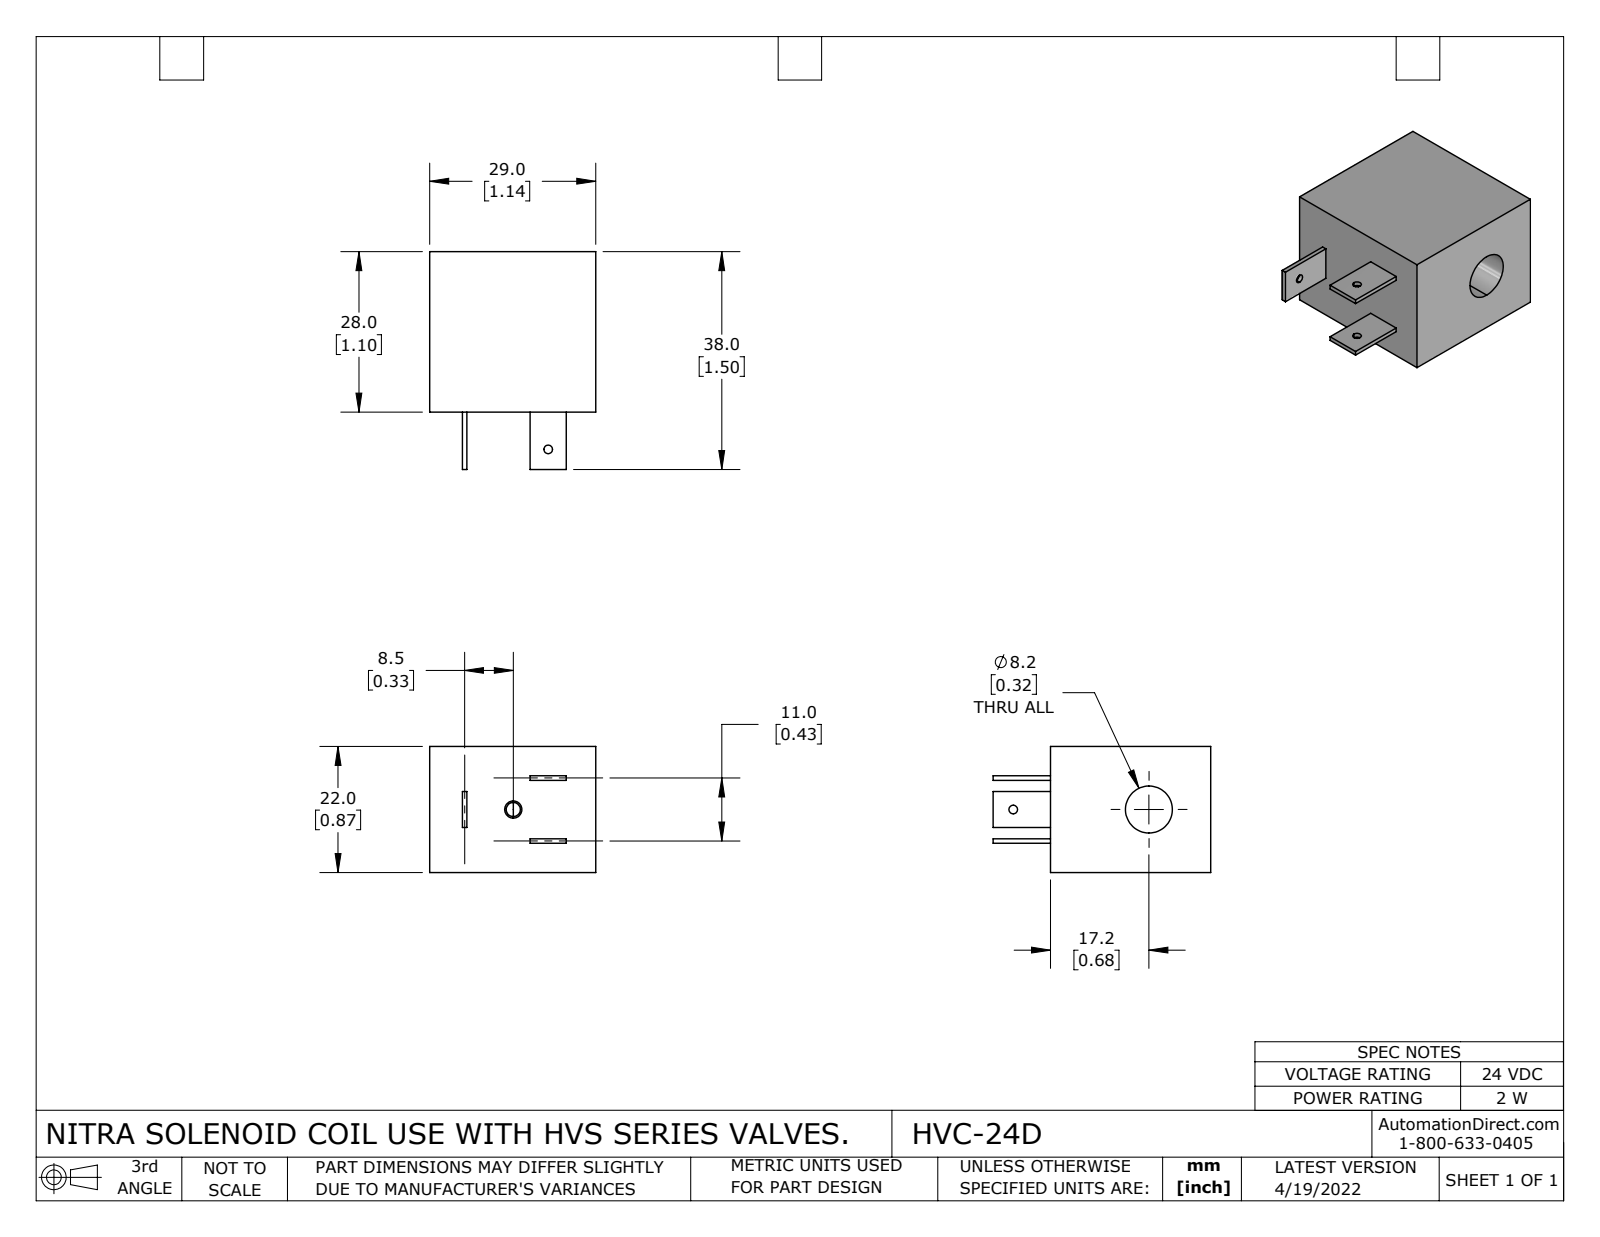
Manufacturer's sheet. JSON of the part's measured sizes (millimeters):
{"part_name": "HVC-24D", "step_written_by": "SolidWorks 2021 (CONFIG_CONTROL_DESIGN)", "units": "millimeters", "bodies": {"solids": 1, "faces": 35, "planar": 21, "cylindrical": 10, "other": 4}, "overall_size": [38, 29, 22], "volume_mm3": 16454, "surface_area_mm2": 5238, "round_holes": [[1.5, 2], [2.46, 1], [8.2, 1]], "face_to_face_distances": [22, 28, 29, 0.8, 5.1, 5.9, 16.1, 16.9, 11, 5.7], "hole_center_spacings": [23.7]}
